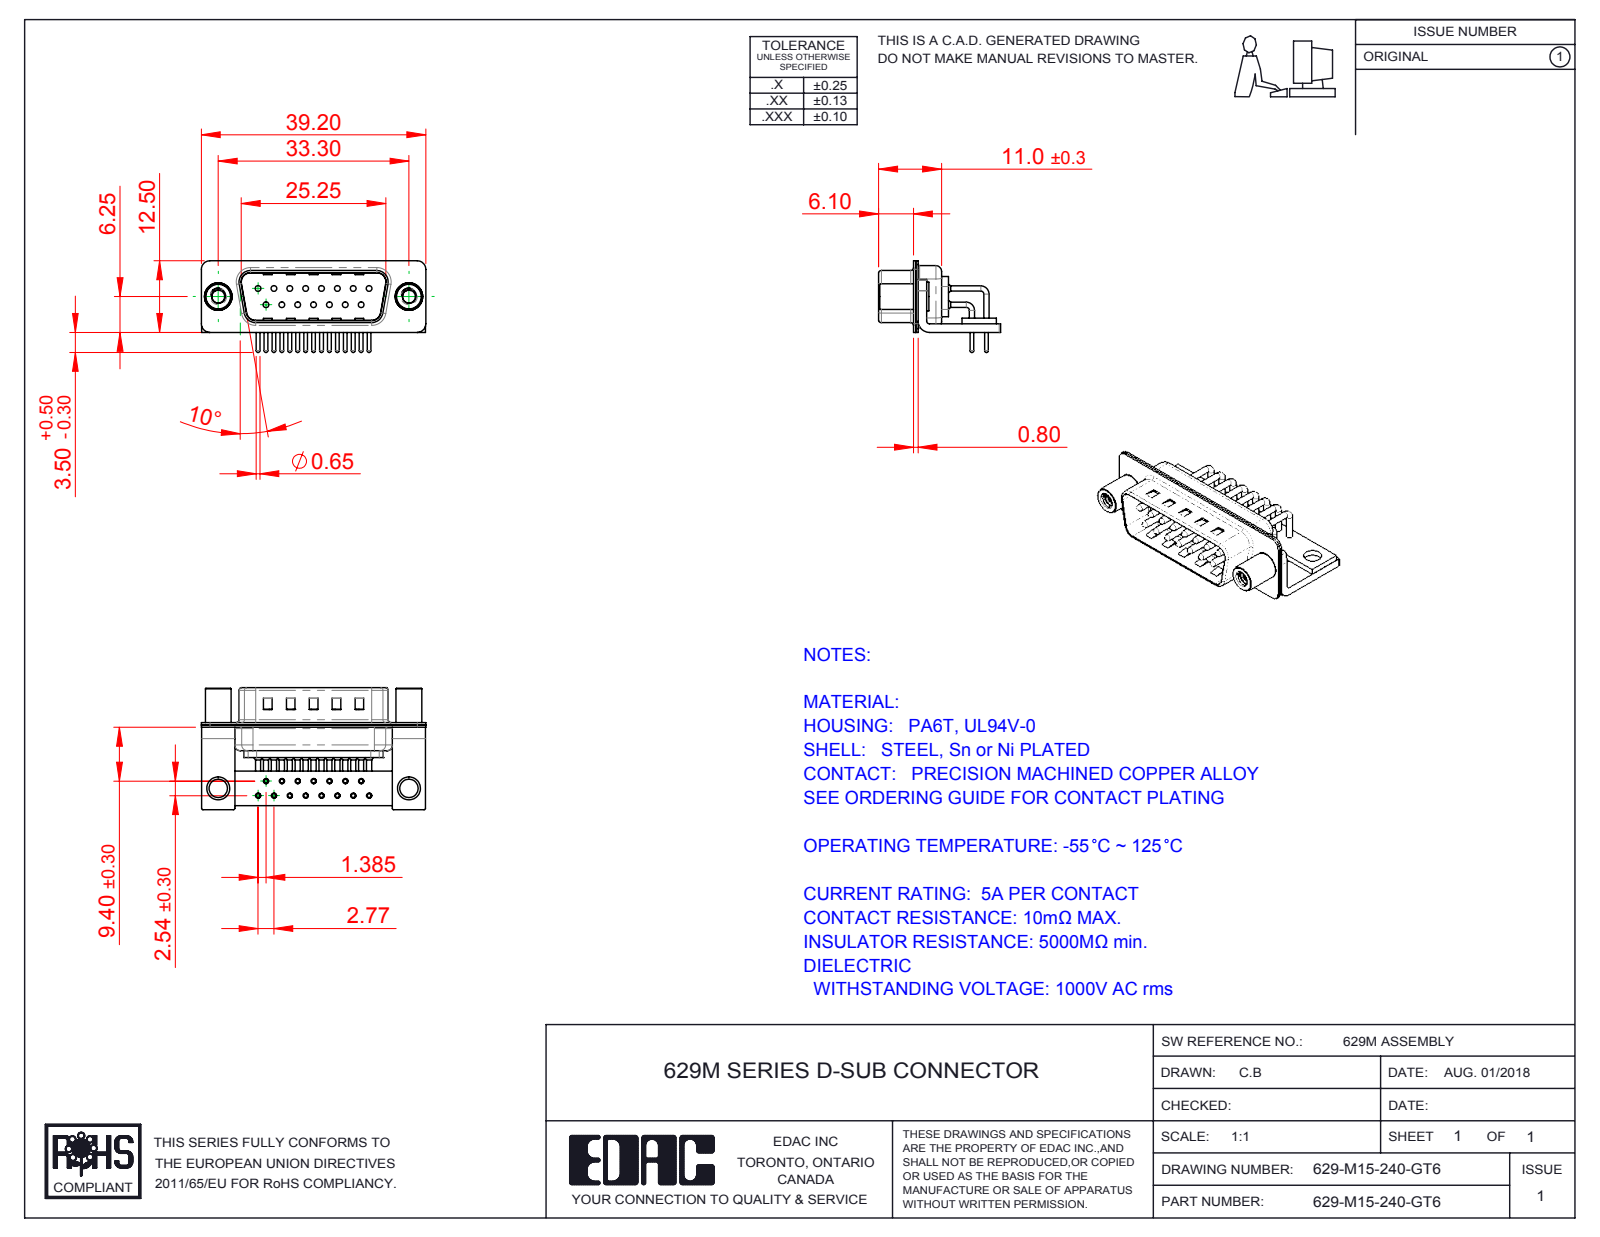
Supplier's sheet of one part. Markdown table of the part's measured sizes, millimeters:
| quantity | value |
| --- | --- |
| part name | 629M Housing_15 Contacts; 629M Shell Front_15 Contacts; 629M Contact Row 1; 629M Shell Rear_15 Contacts (+5 more) |
| STEP written by | SolidWorks 2016 (CONFIG_CONTROL_DESIGN) |
| units | millimeters |
| bodies | 23 solids, 2120 faces (1127 planar, 767 cylindrical, 226 other) |
| overall size | 39.2 × 21.3 × 16 |
| volume | 2 563 mm³ |
| surface area | 6 845 mm² |
| round holes (diameter × count) | 0.9 × 15, 1 × 15, 1.7 × 15, 2 × 15, 2.26 × 2, 3.2 × 2, 4 × 2, 4.8 × 2 |
| round bosses / shafts (diameter × count) | 0.9 × 21, 1.5 × 15, 0.65 × 15, 5 × 2, 4.9 × 2, 4.5 × 2 |
| partial cylindrical surfaces (radius × count) | 0.25 × 16, 1.5 × 16, 1.01 × 15, 2 × 13, 0.5 × 9, 1.6 × 8, 0.6 × 4, 0.65 × 4 |
| main face-to-face distances | 0.4, 1.5, 0.85, 0.8, 1.25, 10.4, 9.55, 1.9, 1, 8.3 |
| hole center spacings | 2.77, 5.54, 3.16, 8.31, 4.87, 11.08, 2.89, 7.37 |
